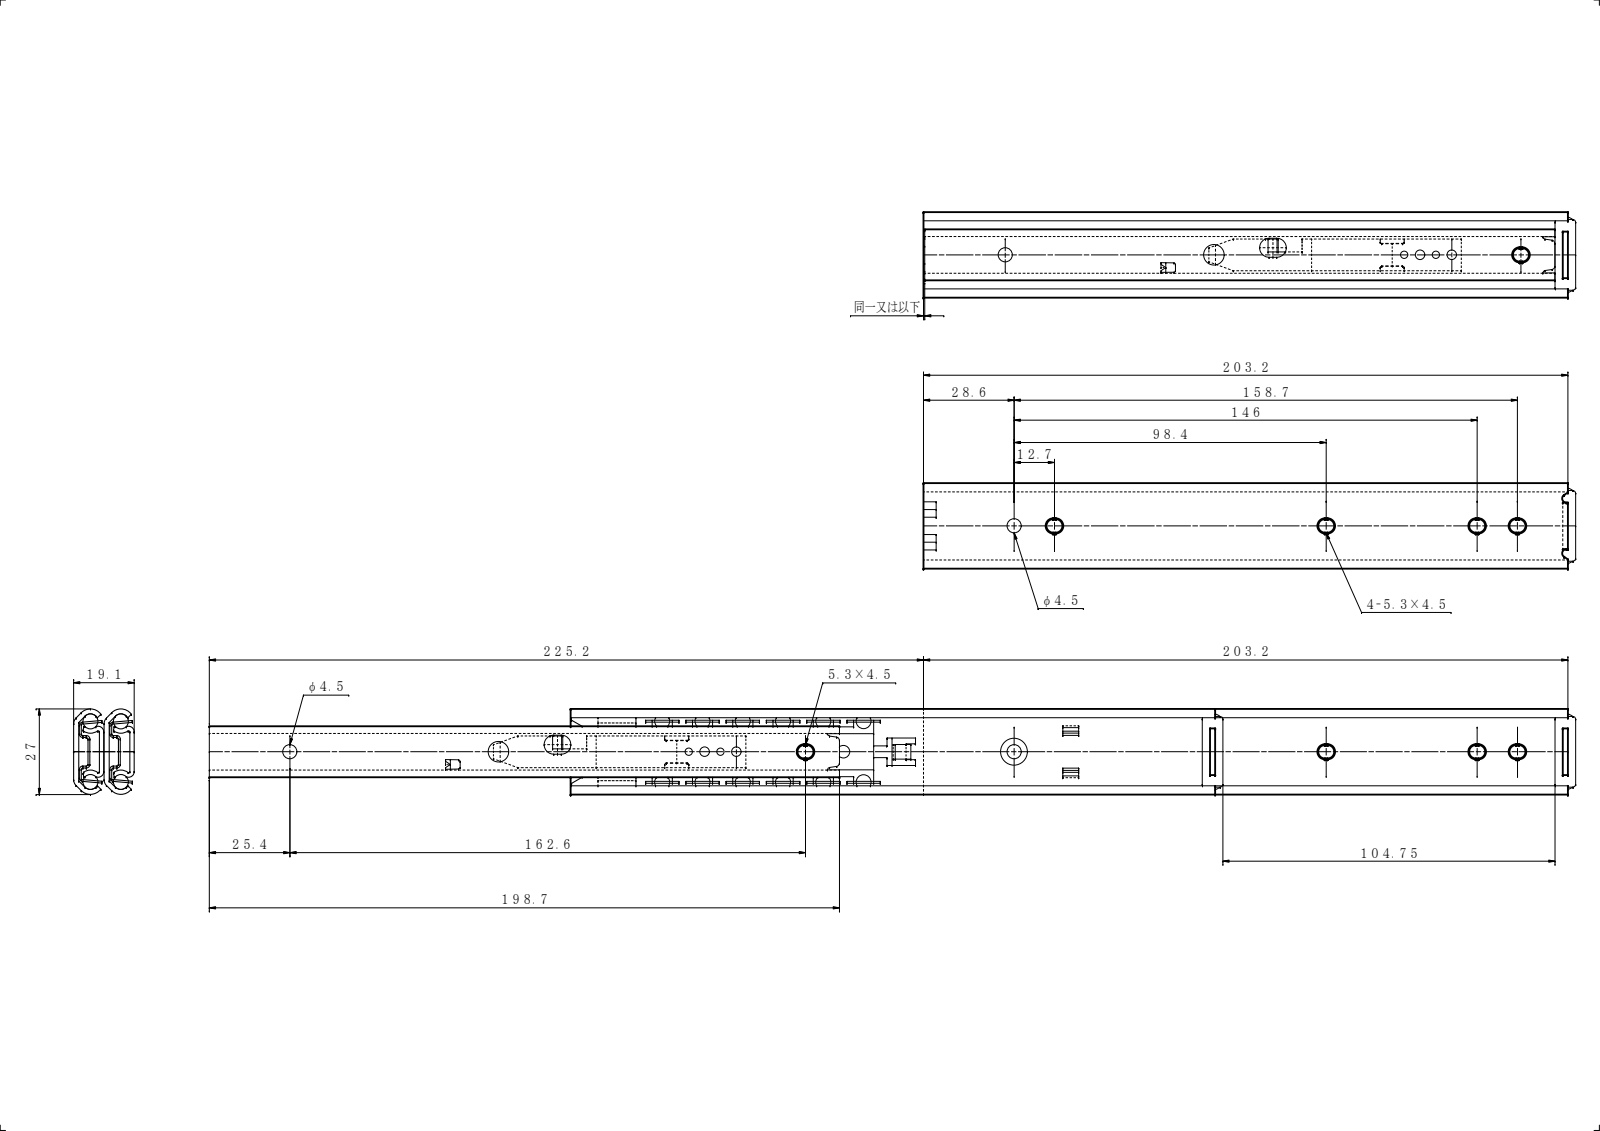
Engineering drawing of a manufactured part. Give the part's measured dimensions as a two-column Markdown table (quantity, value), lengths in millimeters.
| quantity | value |
| --- | --- |
| part name | IM-B 2736-8; OM-B 2736-8; OM-A 2736-8; SBP806 リードイン (+4 more) |
| STEP written by | SolidWorks 2019 (CONFIG_CONTROL_DESIGN) |
| units | millimeters |
| bodies | 8 solids, 360 faces (158 planar, 182 cylindrical, 20 other) |
| overall size | 430.9 × 27 × 19 |
| volume | 39 049 mm³ |
| surface area | 55 476 mm² |
| round holes (diameter × count) | 2.34 × 2, 2.9 × 2, 3.03 × 2, 4.5 × 2, 4 × 1, 4.2 × 1, 4.3 × 1, 6.5 × 1, 8.5 × 1 |
| round bosses / shafts (diameter × count) | 4.5 × 2, 4.3 × 2, 4.25 × 2, 3.9 × 2 |
| partial cylindrical surfaces (radius × count) | 0.2 × 26, 2 × 23, 1 × 10, 2.25 × 10, 3 × 8, 0.28 × 4, 0.5 × 4, 1.68 × 4 |
| main face-to-face distances | 9.5, 1.6, 7.9, 6.5, 1.4, 8.1, 11.1, 17.6, 16, 19 |
| hole center spacings | 5, 10, 15, 21.35, 21.4, 22.75, 27.65, 32.58 |
